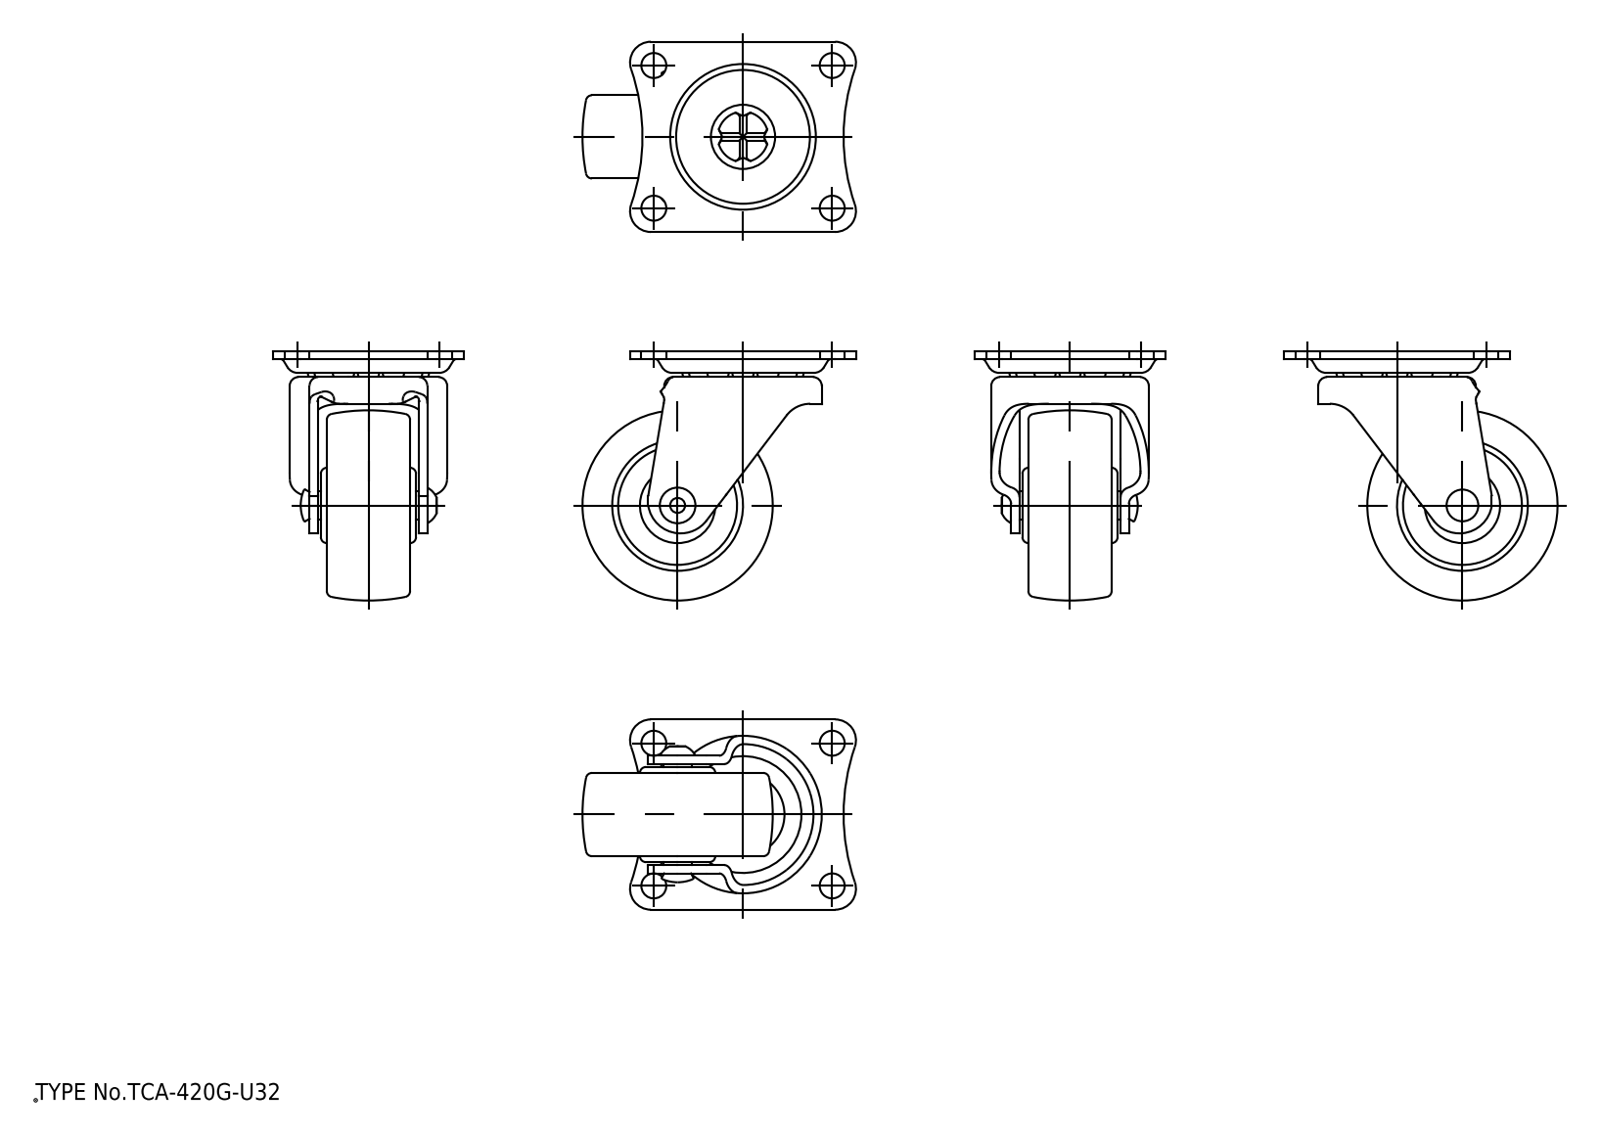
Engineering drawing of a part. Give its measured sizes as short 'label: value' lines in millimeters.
name: wheel; mounting plate; main shaft; axle
written by: spGate 19.8.4 (****-****-****-****) (AUTOMOTIVE_DESIGN)
unit: mm
bodies: 5 solids, 248 faces (68 planar, 76 cylindrical, 104 other)
size: 46 × 42 × 32
volume: 15 081 mm³; area: 10 288 mm²
holes: 4× ⌀4.2, 1× ⌀4.8, 1× ⌀7, 1× ⌀23.7
bosses: 1× ⌀26.5, 1× ⌀12.68, 1× ⌀10
rounds: 10× R0.5, 6× R2, 4× R3, 4× R3.5, 2× R0.2, 2× R35, 1× R1, 1× R4.25
face distances: 1.4, 4.4, 1, 14, 5.8, 13, 3, 1.5, 2.5, 14.5
hole spacings: 19.21, 24, 30, 38.42
